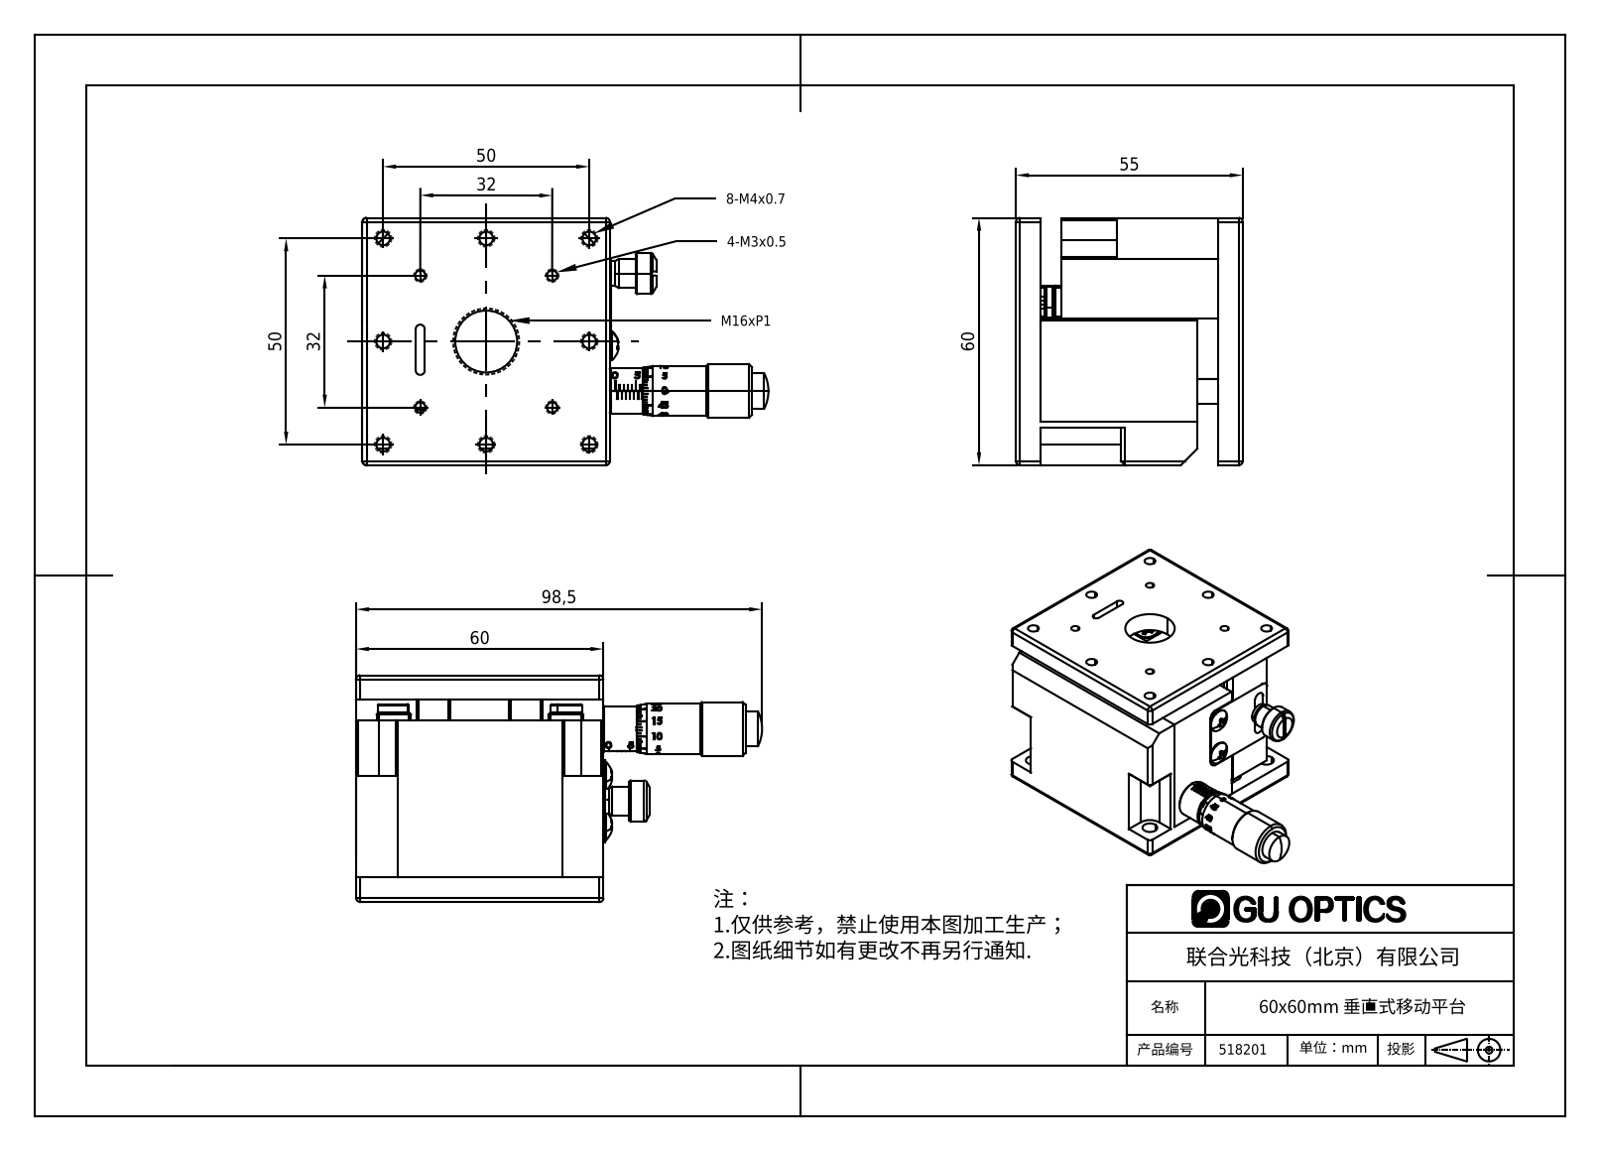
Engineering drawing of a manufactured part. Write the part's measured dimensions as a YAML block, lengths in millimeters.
part_name: "MZA-60"
step_written_by: "SolidWorks 2020 (CONFIG_CONTROL_DESIGN)"
units: millimeters
bodies: {solids: 16, faces: 1157, planar: 613, cylindrical: 219, other: 325}
overall_size: [98.5, 60, 55]
volume: 158280
surface_area: 51616
round_holes:
  - {diameter: 3.3, count: 8}
  - {diameter: 2.5, count: 5}
  - {diameter: 4.5, count: 4}
  - {diameter: 3.5, count: 2}
  - {diameter: 11, count: 1}
  - {diameter: 15, count: 1}
round_bosses_or_shafts:
  - {diameter: 3, count: 8}
  - {diameter: 7.5, count: 4}
  - {diameter: 9, count: 2}
  - {diameter: 6.9, count: 2}
  - {diameter: 6, count: 2}
  - {diameter: 13, count: 1}
  - {diameter: 12.1, count: 1}
  - {diameter: 10, count: 1}
partial_cylinders:
  - {radius: 1, count: 17}
  - {radius: 2.5, count: 8}
  - {radius: 4, count: 7}
  - {radius: 1.1, count: 4}
  - {radius: 2, count: 4}
  - {radius: 1.75, count: 2}
  - {radius: 3, count: 2}
  - {radius: 5.49, count: 1}
face_to_face_distances: [6, 49, 11, 60, 25, 44, 24.5, 55, 5, 0.5]
hole_center_spacings: [25, 50, 41.98, 18.36, 35.36, 44.01, 55.9, 12.73]
